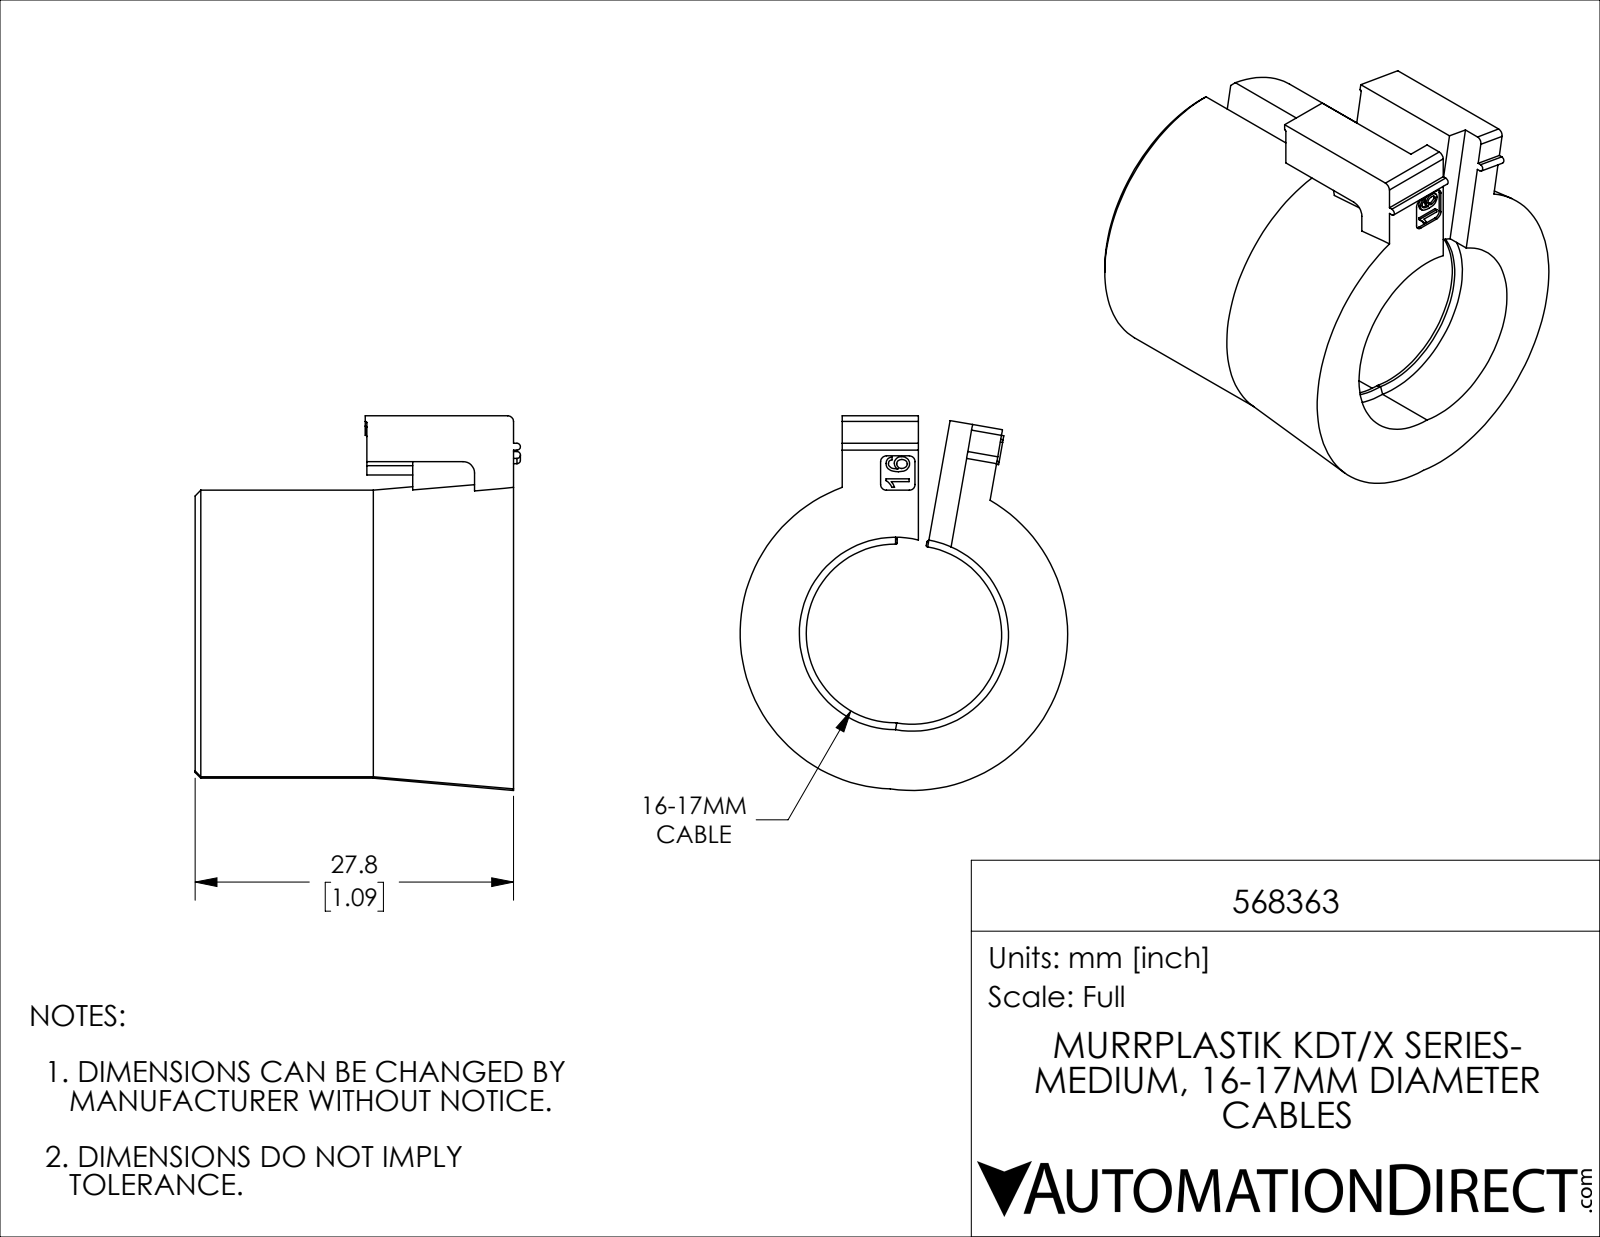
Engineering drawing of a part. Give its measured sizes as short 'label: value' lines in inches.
name: 568363
written by: SolidWorks 2019 (CONFIG_CONTROL_DESIGN)
unit: in
bodies: 1 solid, 125 faces (69 planar, 29 cylindrical, 27 other)
size: 1.287 × 1.126 × 1.118
volume: 0.524 in³; area: 7.919 in²
rounds: 6× R0.004, 6× R0.02, 2× R0.012, 2× R0.039, 2× R0.307, 2× R0.331, 2× R0.492
face distances: 1.094, 0.079, 0.157, 0.183, 0.183, 1.016, 0.504, 0.425, 0.591, 0.104
